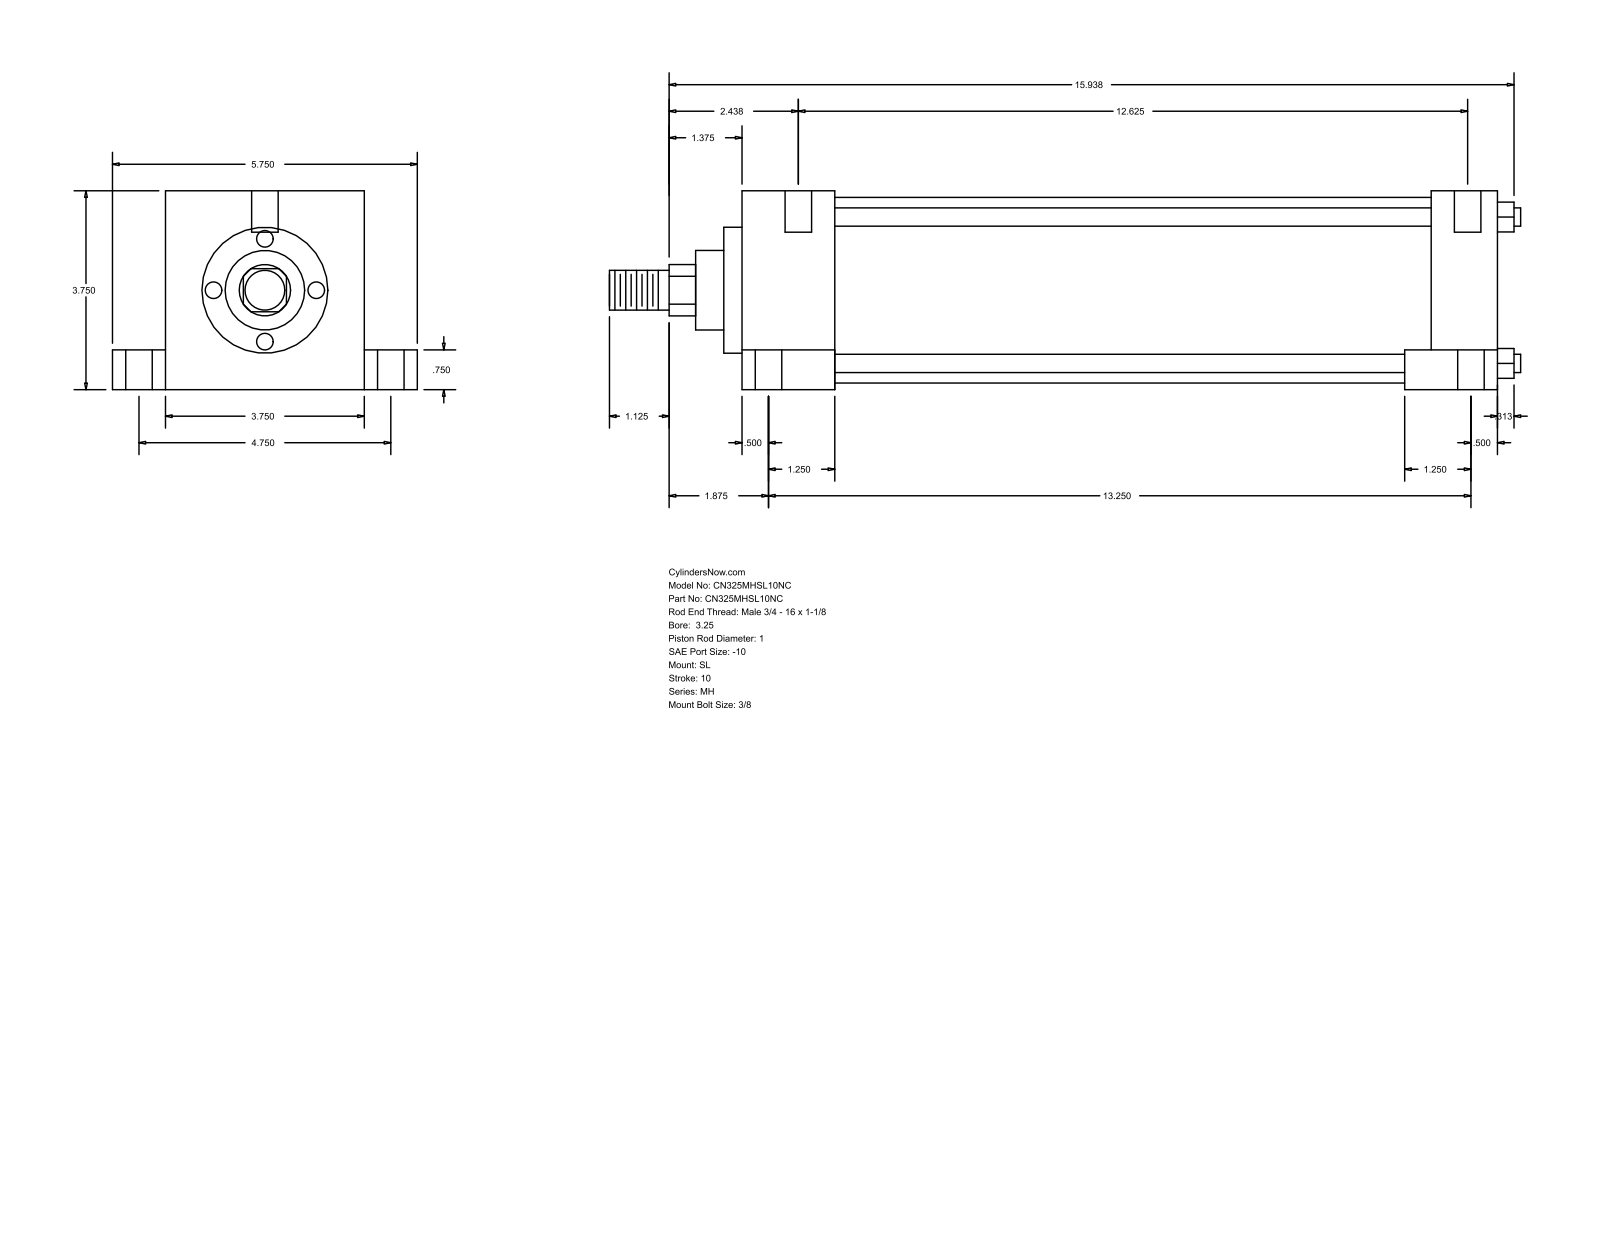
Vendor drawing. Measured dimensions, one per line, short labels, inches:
name: MH_SL__0325_1
written by: GSSL Pune (CONFIG_CONTROL_DESIGN)
unit: in
bodies: 0 solids, 110 faces (77 planar, 33 cylindrical, 0 other)
size: 17.187 × 5.75 × 3.75
holes: 6× ⌀0.5, 4× ⌀0.219, 4× ⌀0.75
bosses: 4× ⌀0.345, 1× ⌀3.5, 1× ⌀2.375, 1× ⌀1.5, 1× ⌀1, 1× ⌀0.75
rounds: 1× R0.484
face distances: 3.75, 14.25, 1.75, 12.5, 1, 4.75, 0.75, 3, 13, 11.25
hole spacings: 2.376, 2.378, 2.427, 2.441, 4.75, 12.875, 12.908, 12.969
